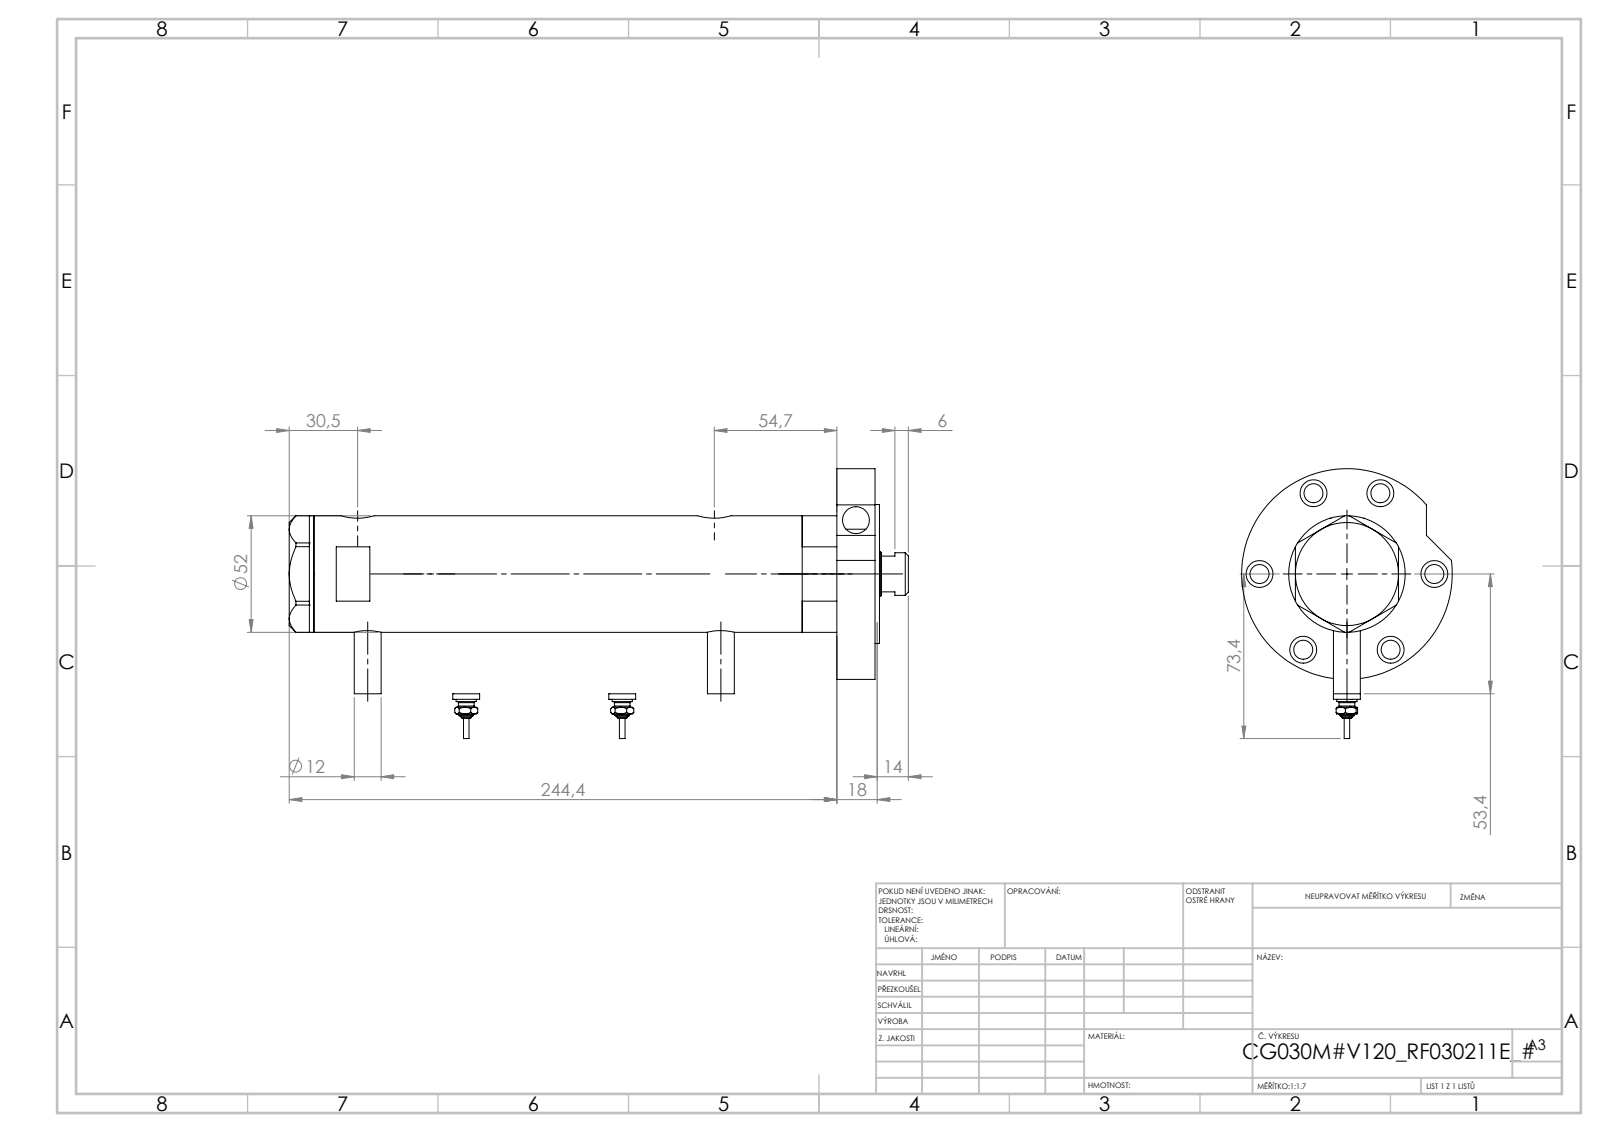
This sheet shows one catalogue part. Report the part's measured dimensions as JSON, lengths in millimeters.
{"part_name": "V270CG_BACK; V270CG_RF211E; V270CG_MIDDLE; V270CG_VC (+2 more)", "step_written_by": "SolidWorks 2019 (CONFIG_CONTROL_DESIGN)", "units": "millimeters", "bodies": {"solids": 7, "faces": 270, "planar": 104, "cylindrical": 102, "other": 64}, "overall_size": [276.3, 120.4, 94], "volume_mm3": 579880, "surface_area_mm2": 132713, "round_holes": [[12, 7], [8.5, 6], [9.73, 2], [12.5, 2], [15, 2], [6.5, 1], [20, 1], [21.5, 1], [30, 1], [33, 1], [40, 1], [44, 1]], "round_bosses_or_shafts": [[12, 4], [9, 2], [7, 2], [4.5, 2], [2.5, 2], [94, 1], [62, 1], [52, 1]], "face_to_face_distances": [17, 233.4, 250.4, 2, 252.4, 181.5, 51.9, 68.9, 70.9, 19], "hole_center_spacings": [39, 43.34, 64.85, 67.55, 69.95, 77.83, 2.9, 4.5]}
